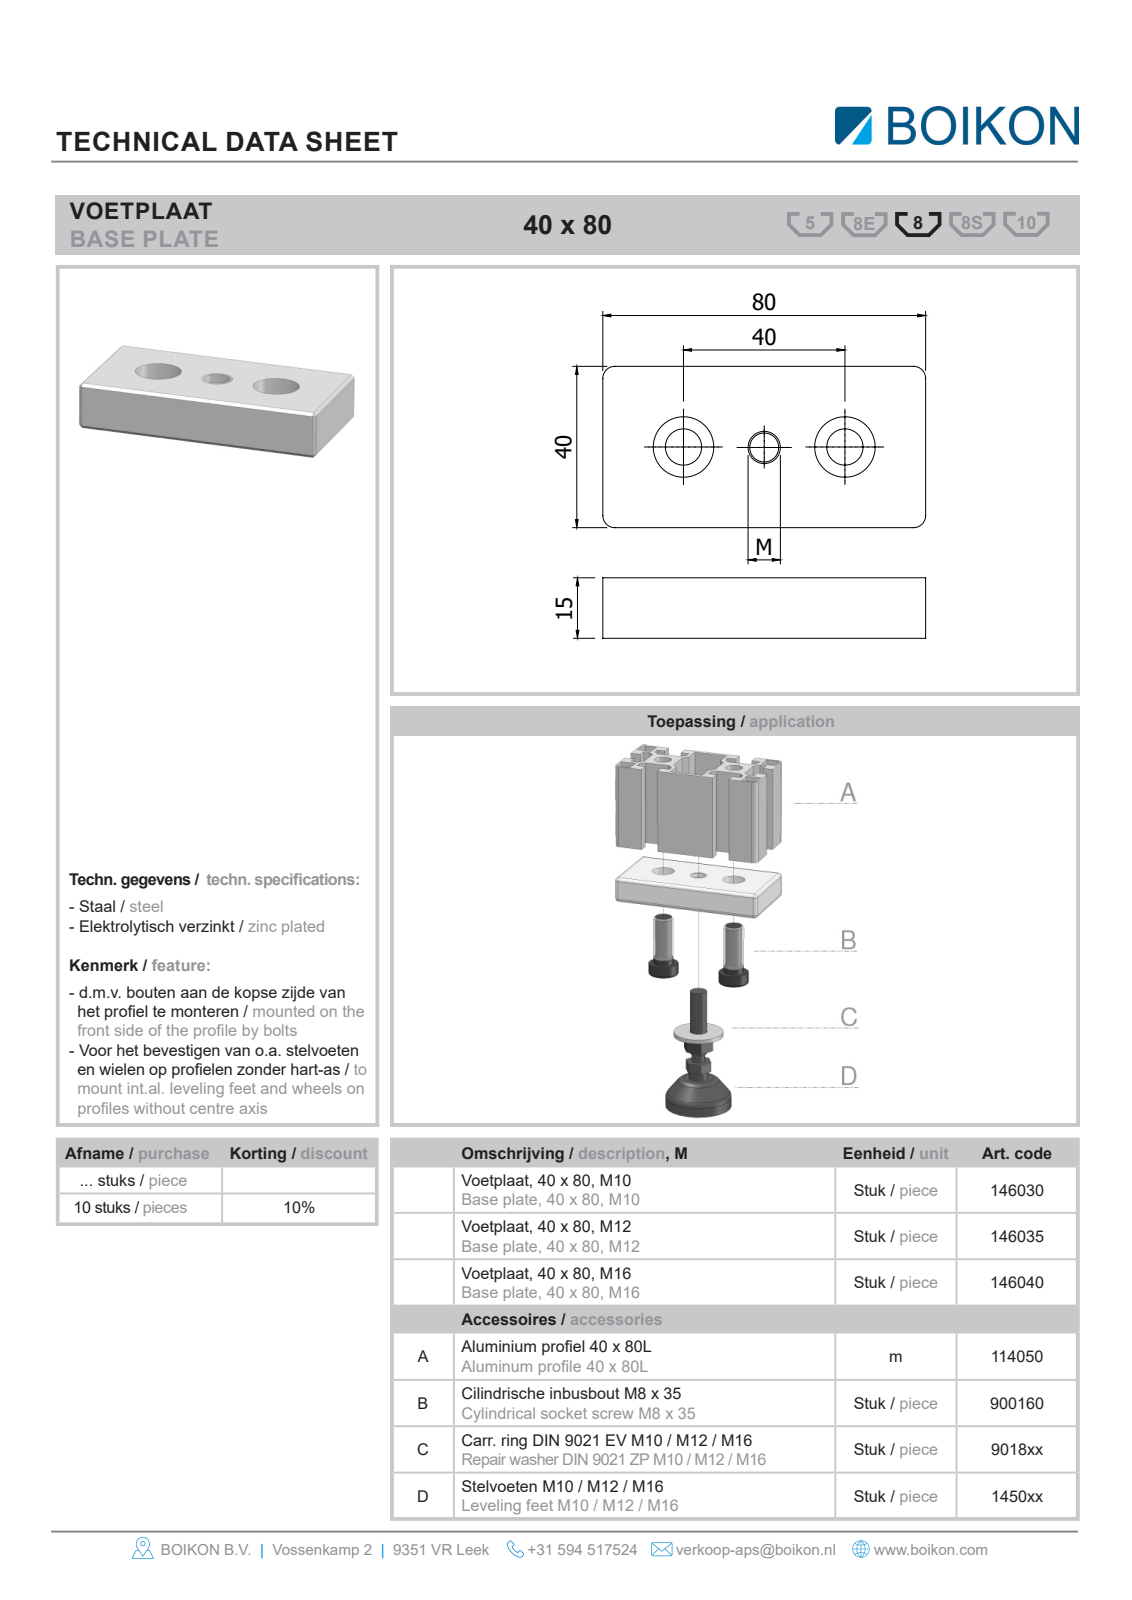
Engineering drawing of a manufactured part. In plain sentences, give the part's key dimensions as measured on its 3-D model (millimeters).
The part is named "Root; 146040Voetplaat 40x80 M16BOIKON; 900160Cil. inbusbout DIN 912 EV M8 x 35BOIKON0". Its 3-D file was written by "HiCAD 2013 1802.4 Build 509 (AUTOMOTIVE_DESIGN)". It is 3 solids with 55 faces: 38 planar, 11 cylindrical and 6 other. Overall it measures 80 by 43.2 by 40 millimeters. Its volume is 45 455 cubic millimeters and its surface area 14 011 square millimeters. Round holes: 2 of diameter 9, 2 of diameter 15, 1 of diameter 16. Round bosses or shafts: 2 of diameter 13, 2 of diameter 8, 2 of diameter 6.47. The main face-to-face distances are 15, 40, 80, 6.8, 8.2, 14.8, 8, 6, 28.2, 35. The hole center spacings are 20, 40.
